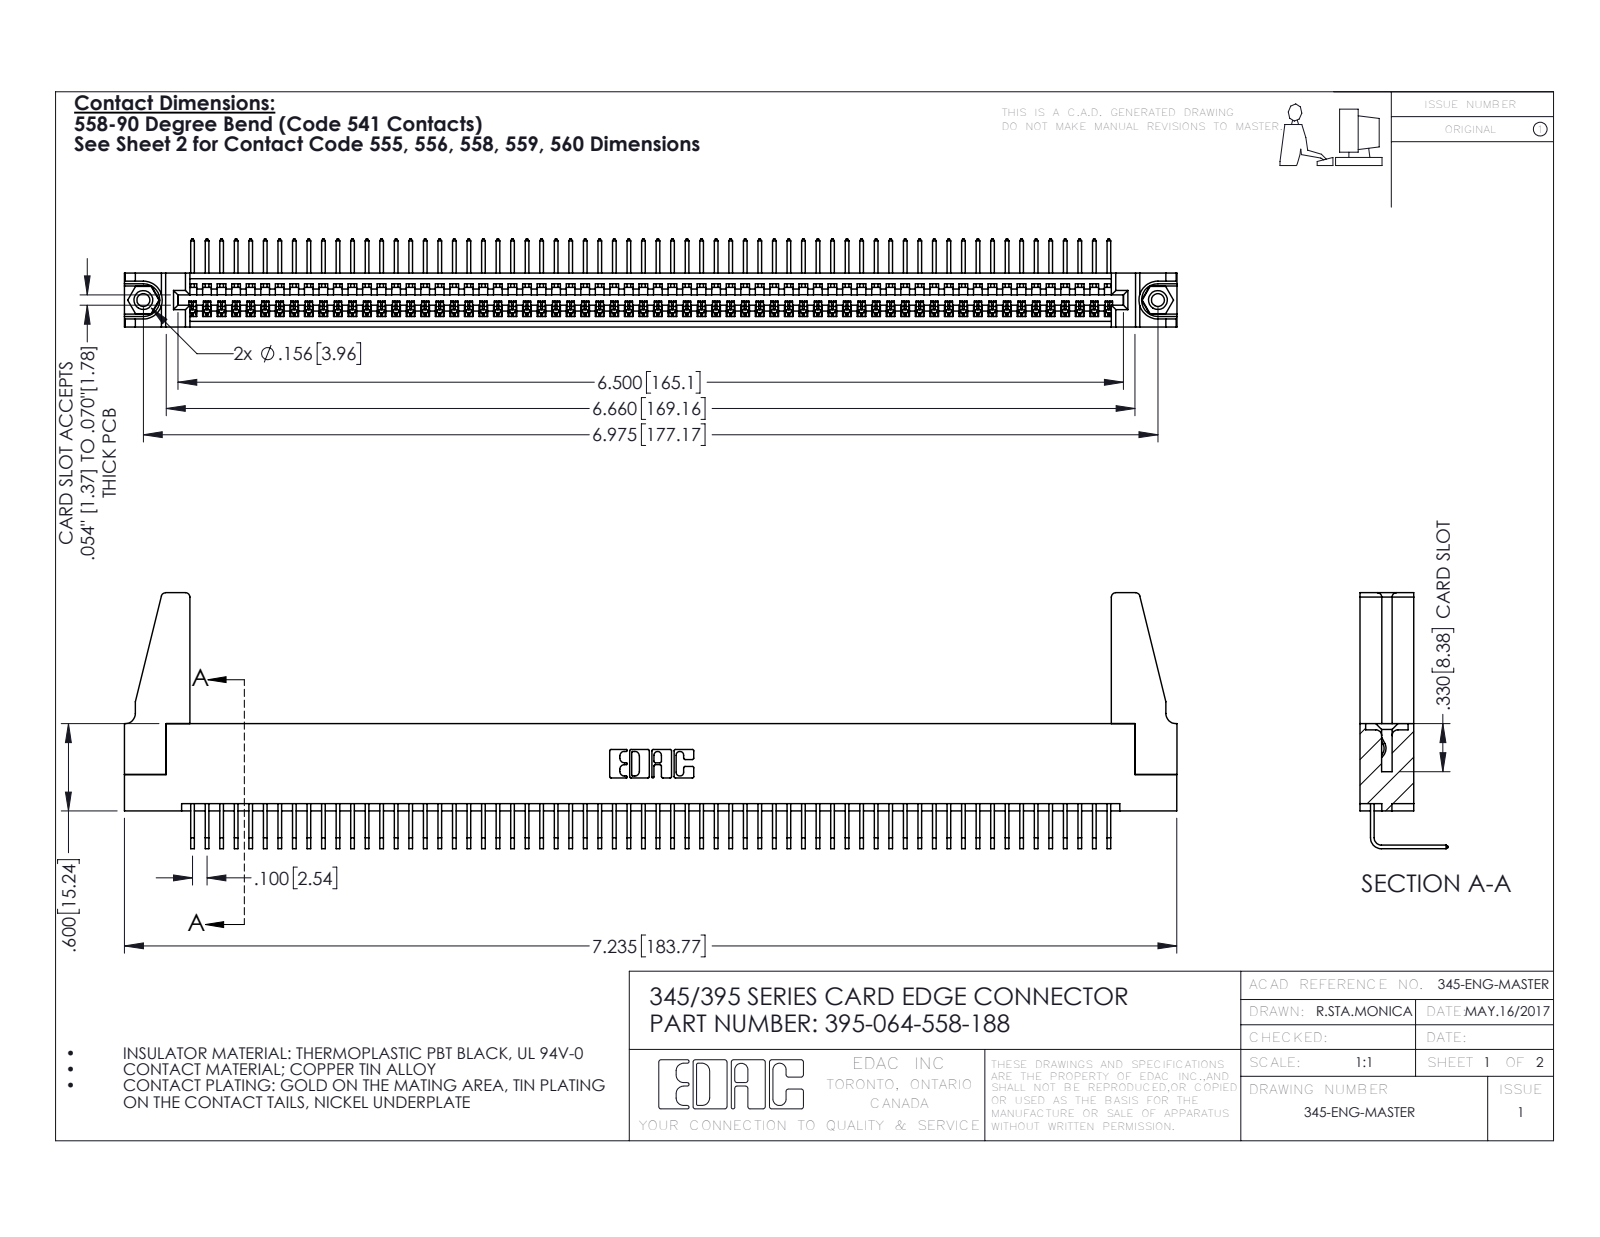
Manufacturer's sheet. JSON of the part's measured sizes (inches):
{"part_name": "345 Part_Flush Mounting Lugs - 0.156 Dia-TH; 345-220-078_345-220-088; 345-292-001_558 Tail - 2; 345-250-001_345-250-001-102 (+1 more)", "step_written_by": "SolidWorks 2016 (CONFIG_CONTROL_DESIGN)", "units": "inches", "bodies": {"solids": 69, "faces": 4090, "planar": 2840, "cylindrical": 1234, "other": 16}, "overall_size": [7.236, 1.759, 0.605], "volume_in3": 1.288, "surface_area_in2": 44.02, "round_holes": [[0.089, 2], [0.125, 2], [0.156, 2], [0.064, 1]], "round_bosses_or_shafts": [[0.155, 2]], "partial_cylinders_radius": [[0.006, 128], [0.01, 22], [0.03, 8], [0.007, 6], [0.031, 6], [0.026, 3], [0.031, 2], [0.04, 2]], "face_to_face_distances": [0.072, 0.298, 0.37, 0.2, 0.098, 0.272, 0.025, 0.225, 0.149, 0.072], "hole_center_spacings": [0.27, 6.739, 6.975]}
